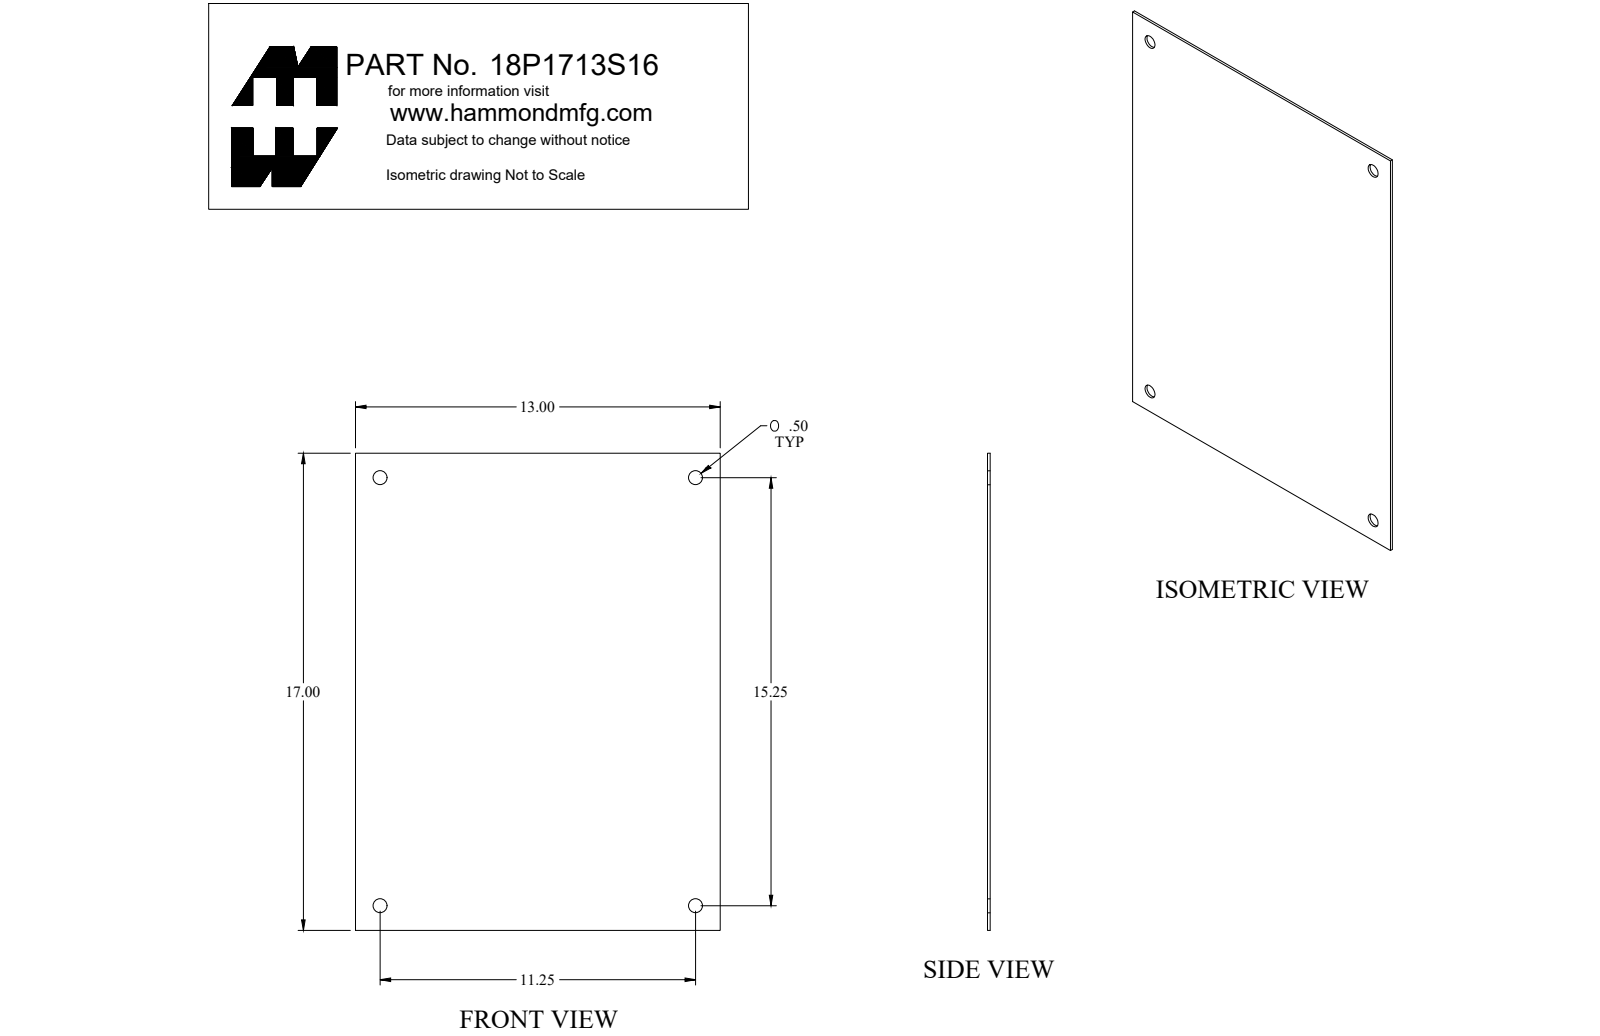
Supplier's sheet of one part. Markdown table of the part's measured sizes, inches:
| quantity | value |
| --- | --- |
| part name | 18P1713S16_Default |
| STEP written by | SolidWorks 2018 (CONFIG_CONTROL_DESIGN) |
| units | inches |
| bodies | 1 solid, 14 faces (6 planar, 8 cylindrical, 0 other) |
| overall size | 17 × 13 × 0.095 |
| volume | 20.92 in³ |
| surface area | 446.7 in² |
| round holes (diameter × count) | 0.5 × 4 |
| main face-to-face distances | 0.095, 13, 17 |
| hole center spacings | 11.25, 15.25, 18.951 |
